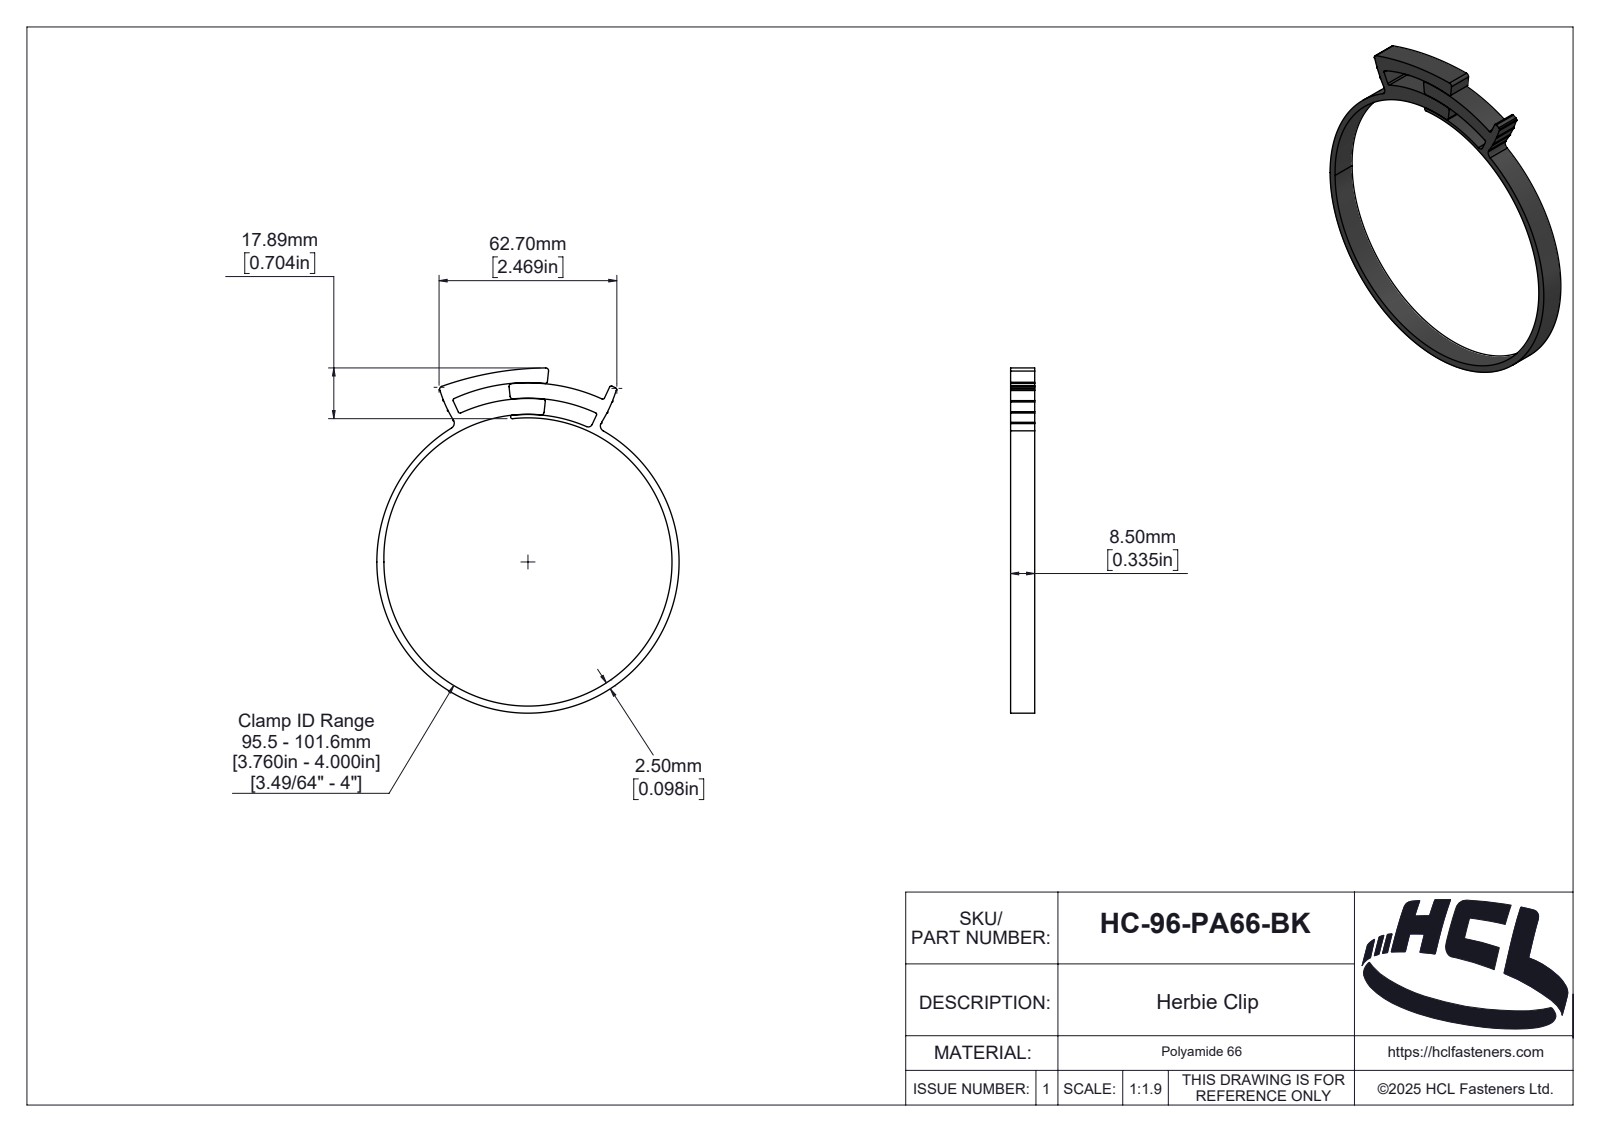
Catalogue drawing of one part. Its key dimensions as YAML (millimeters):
part_name: "HC-96-PA66-BK"
step_written_by: "SolidWorks 2025 (AUTOMOTIVE_DESIGN)"
units: millimeters
bodies: {solids: 1, faces: 162, planar: 13, cylindrical: 100, other: 49}
overall_size: [121.69, 106.6, 8.5]
volume: 11317
surface_area: 10132
partial_cylinders:
  - {radius: 0.25, count: 8}
  - {radius: 0.6, count: 7}
  - {radius: 1, count: 5}
  - {radius: 2, count: 2}
  - {radius: 0.17, count: 1}
  - {radius: 0.67, count: 1}
  - {radius: 0.84, count: 1}
  - {radius: 0.89, count: 1}
face_to_face_distances: [8.5]
